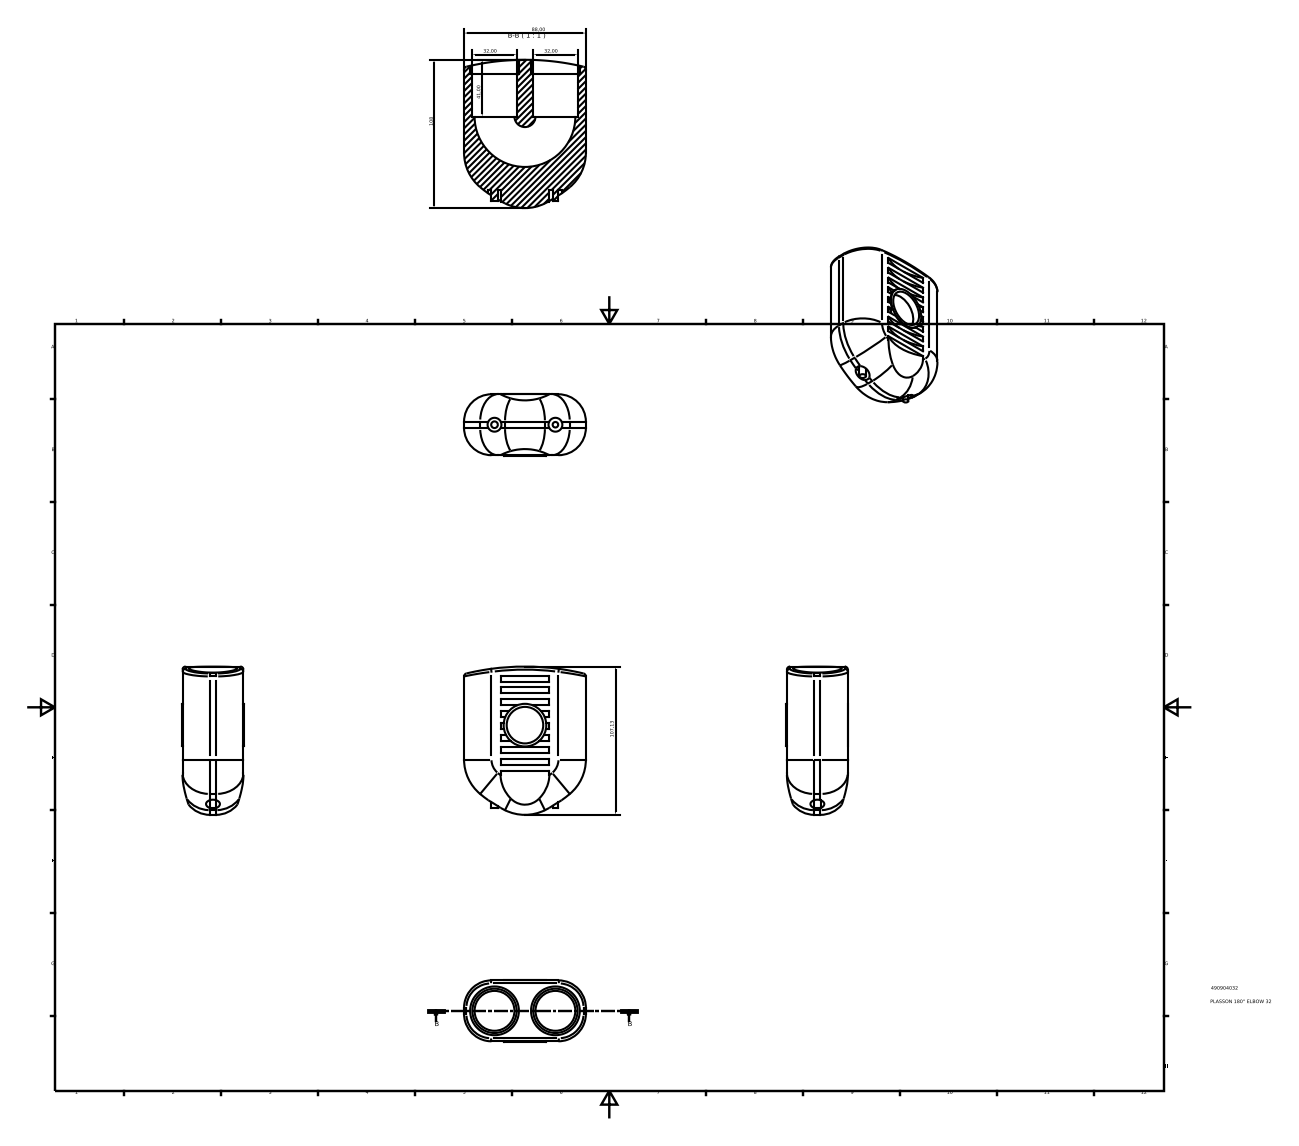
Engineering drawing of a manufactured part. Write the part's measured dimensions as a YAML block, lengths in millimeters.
part_name: "490904032"
step_written_by: "Autodesk Inventor 2015 (AUTOMOTIVE_DESIGN)"
units: millimeters
bodies: {solids: 1, faces: 131, planar: 64, cylindrical: 50, other: 17}
overall_size: [107.13, 88, 44.88]
volume: 202496
surface_area: 44068
round_holes:
  - {diameter: 10, count: 2}
  - {diameter: 32, count: 2}
  - {diameter: 35.2, count: 2}
  - {diameter: 26.4, count: 1}
round_bosses_or_shafts:
  - {diameter: 30.8, count: 1}
  - {diameter: 4.8, count: 1}
  - {diameter: 4, count: 1}
partial_cylinders:
  - {radius: 19.8, count: 4}
  - {radius: 32.4, count: 3}
  - {radius: 2.2, count: 2}
  - {radius: 37.4, count: 2}
  - {radius: 91.73, count: 2}
  - {radius: 181.96, count: 1}
face_to_face_distances: [44, 4.32, 8.64, 5.5, 38.5, 12.96, 51.84, 47.52, 56.16, 43.2]
hole_center_spacings: [44]
